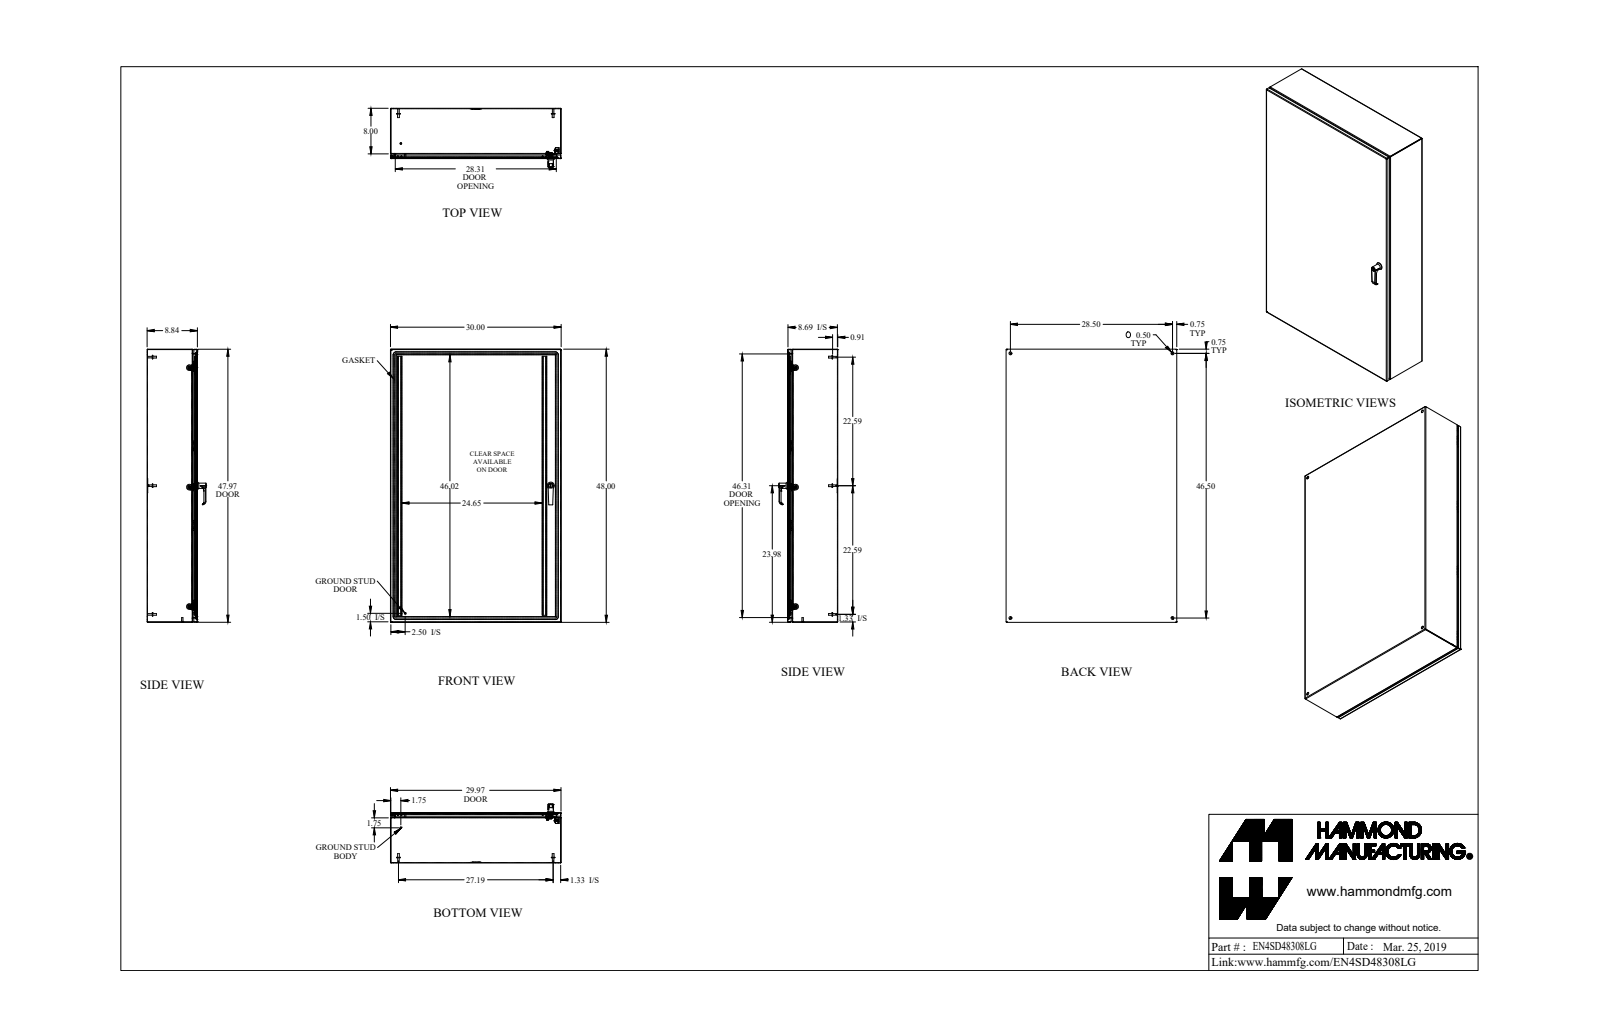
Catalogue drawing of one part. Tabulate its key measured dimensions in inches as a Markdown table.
| quantity | value |
| --- | --- |
| part name | EN4SD48308LG_Default |
| STEP written by | SolidWorks 2019 (CONFIG_CONTROL_DESIGN) |
| units | inches |
| bodies | 53 solids, 1457 faces (632 planar, 538 cylindrical, 287 other) |
| overall size | 48 × 30 × 10.367 |
| volume | 350 in³ |
| surface area | 9 713 in² |
| round holes (diameter × count) | 0.176 × 6, 0.5 × 4, 0.196 × 3, 0.25 × 3, 0.265 × 3, 0.413 × 3, 0.256 × 2, 0.313 × 2, 0.394 × 2, 0.172 × 1, 0.24 × 1, 0.242 × 1 |
| round bosses / shafts (diameter × count) | 0.25 × 7, 0.625 × 6, 0.375 × 6, 0.313 × 6, 0.27 × 6, 0.156 × 6, 1 × 3, 0.63 × 2 |
| partial cylindrical surfaces (radius × count) | 0.036 × 20, 0.108 × 20, 0.03 × 15, 0.043 × 12, 0.081 × 12, 0.006 × 8, 0.04 × 8, 0.062 × 8 |
| main face-to-face distances | 0.072, 8.765, 8.693, 8.837, 29.928, 47.928, 29.856, 30, 47.856, 48 |
| hole center spacings | 0.787, 2.507, 20.981, 20.988, 21, 27.52, 28.5, 41.969 |
